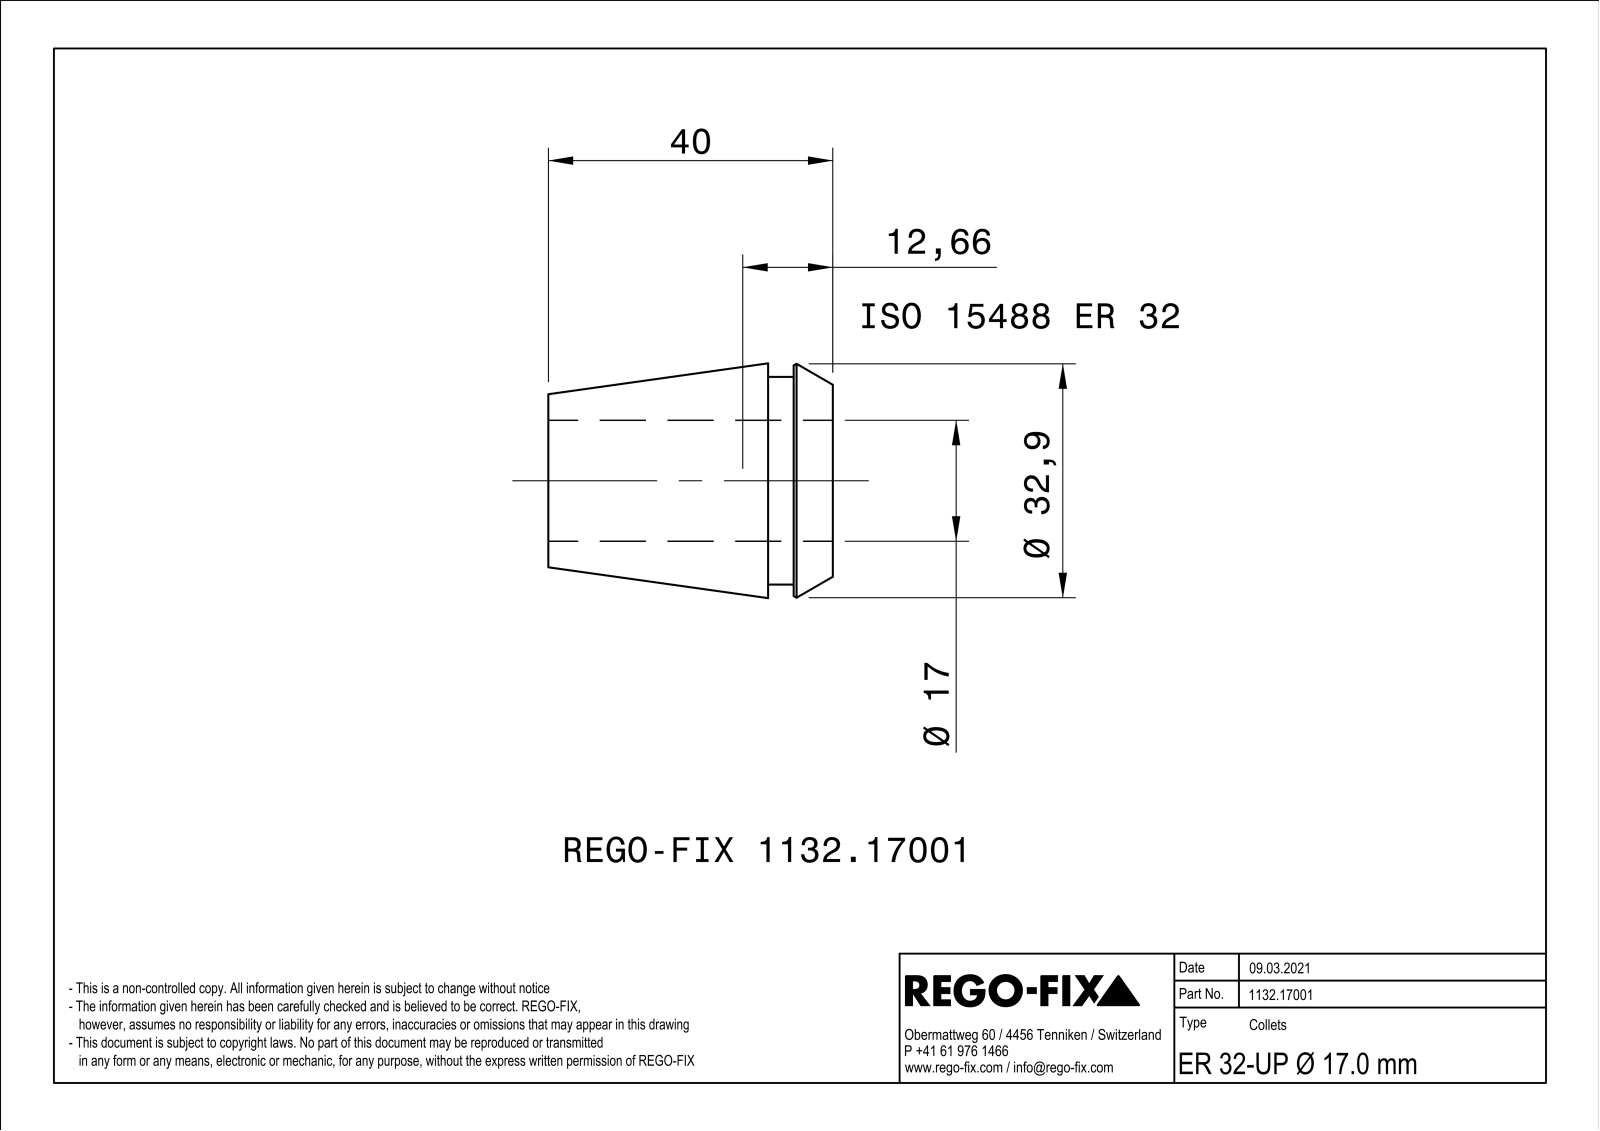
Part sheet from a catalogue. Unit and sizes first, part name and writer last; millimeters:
Units: millimetres
Overall size (bounding box): 40 × 32.98 × 32.98
Round holes (diameter × count): ⌀17 ×1
Round bosses / shafts (diameter × count): ⌀29.2 ×1
Partial cylindrical surfaces — rounded edges, fillets, slot ends (radius × count): R0.4 ×20
Main face-to-face distances: 1, 40, 9.1, 30.9, 5.5, 3.6, 34.5, 6, 0.5, 3.1
Volume: 13 950 mm³ · Surface area: 12 384 mm²
Bodies: 1 solid, 209 faces (88 planar, 41 cylindrical, 80 other)
Part name (STEP PRODUCT): NOCUT
STEP written by: SIEMENS PLM Software Solid Edge ST10 (AUTOMOTIVE_DESIGN)
